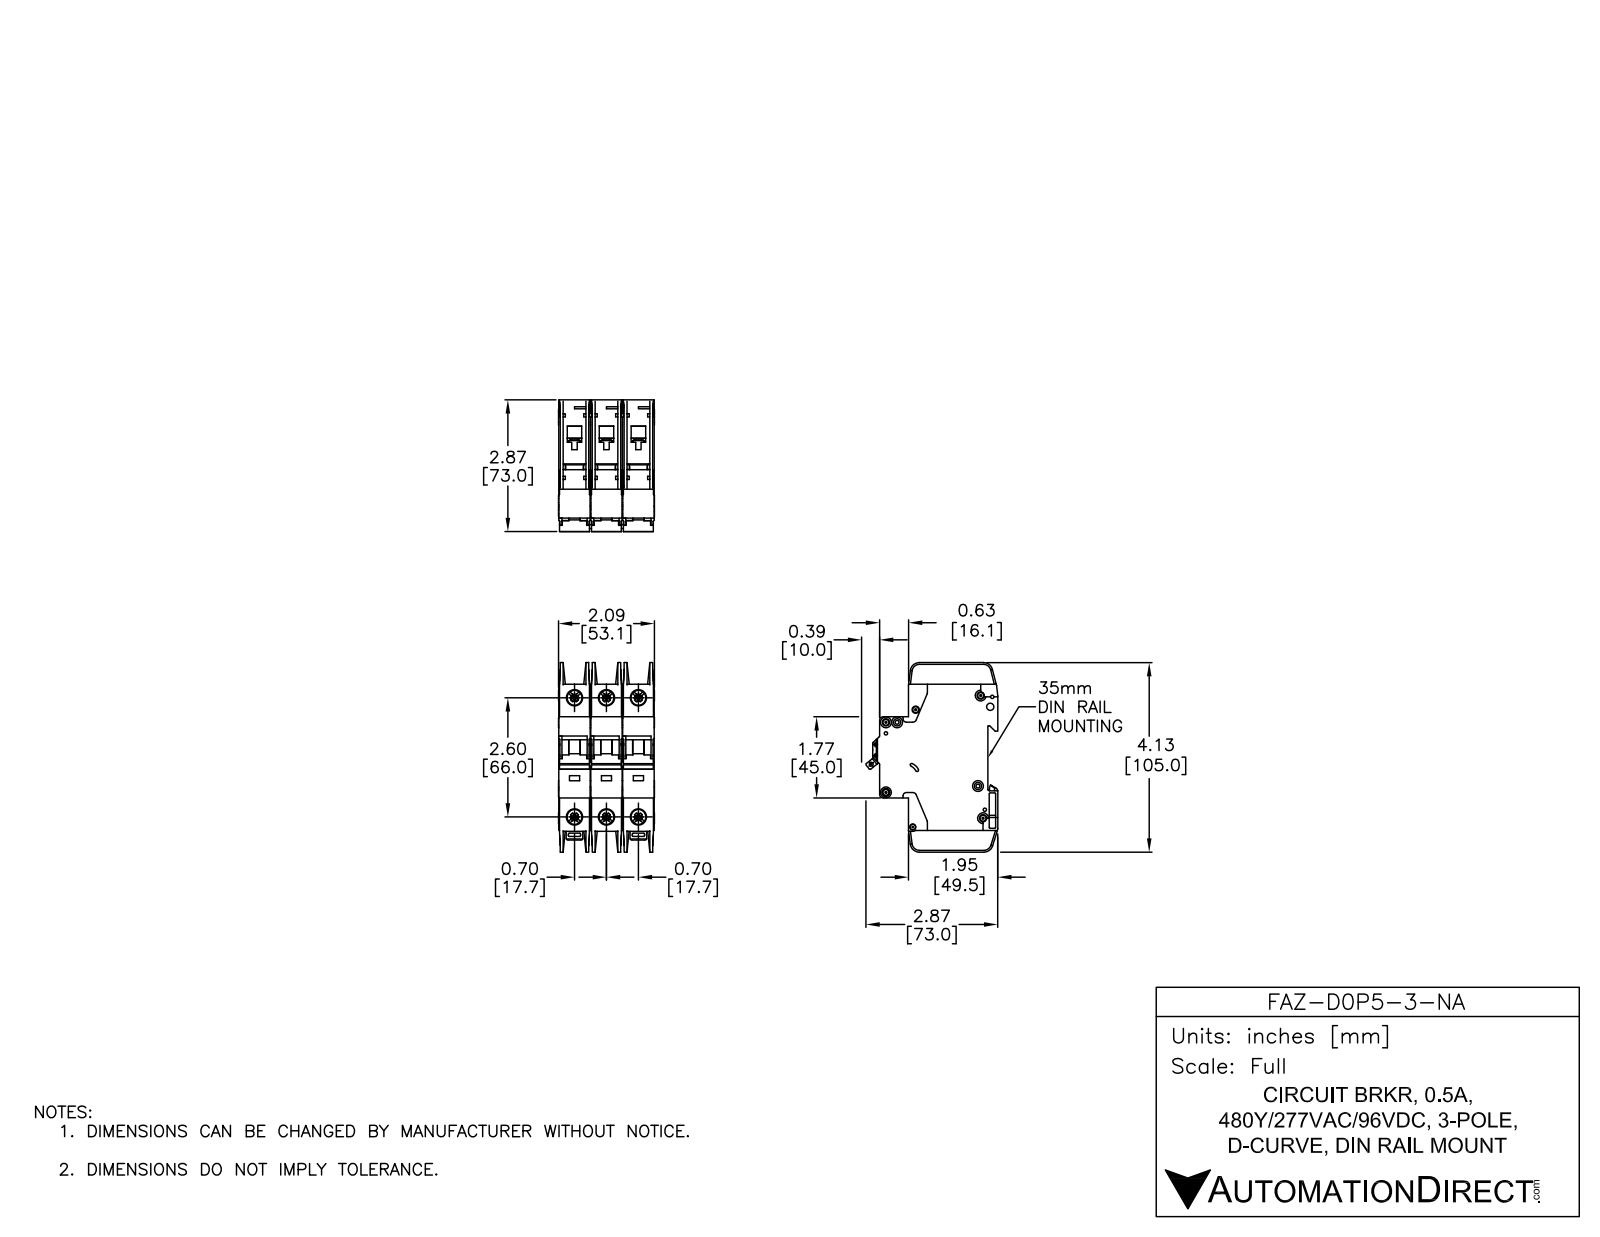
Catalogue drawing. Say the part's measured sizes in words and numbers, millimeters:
The part is named "FAZ-D0P5-3-NA". Its 3-D file was written by "SolidWorks 2014 (AUTOMOTIVE_DESIGN)". It is 9 solids with 2352 faces: 1227 planar, 789 cylindrical and 336 other. Overall it measures 105 by 73.04 by 53.1 millimeters. Its volume is 233 085 cubic millimeters and its surface area 74 219 square millimeters. Round holes: 7 of diameter 3.6, 6 of diameter 7.15, 6 of diameter 8.2, 2 of diameter 1.09, 2 of diameter 1.5, 2 of diameter 4, 1 of diameter 1.9, 1 of diameter 2.15, 1 of diameter 2.2, 1 of diameter 2.55, 1 of diameter 3.3, 1 of diameter 3.4. Round bosses or shafts: 7 of diameter 6, 3 of diameter 2.5. Partial cylindrical surfaces (rounded edges, fillets, slot ends): 65 of radius 0.25, 30 of radius 0.5, 26 of radius 1, 14 of radius 2, 5 of radius 1.8, 5 of radius 5, 4 of radius 4, 2 of radius 0.2. The main face-to-face distances are 17.7, 35.4, 17.5, 35.2, 0.7, 15.05, 2.45, 1.75, 15.75, 13.3. The hole center spacings are 17.7, 68.33, 66, 6.2, 35.4, 74.89, 5.19, 6.1.
